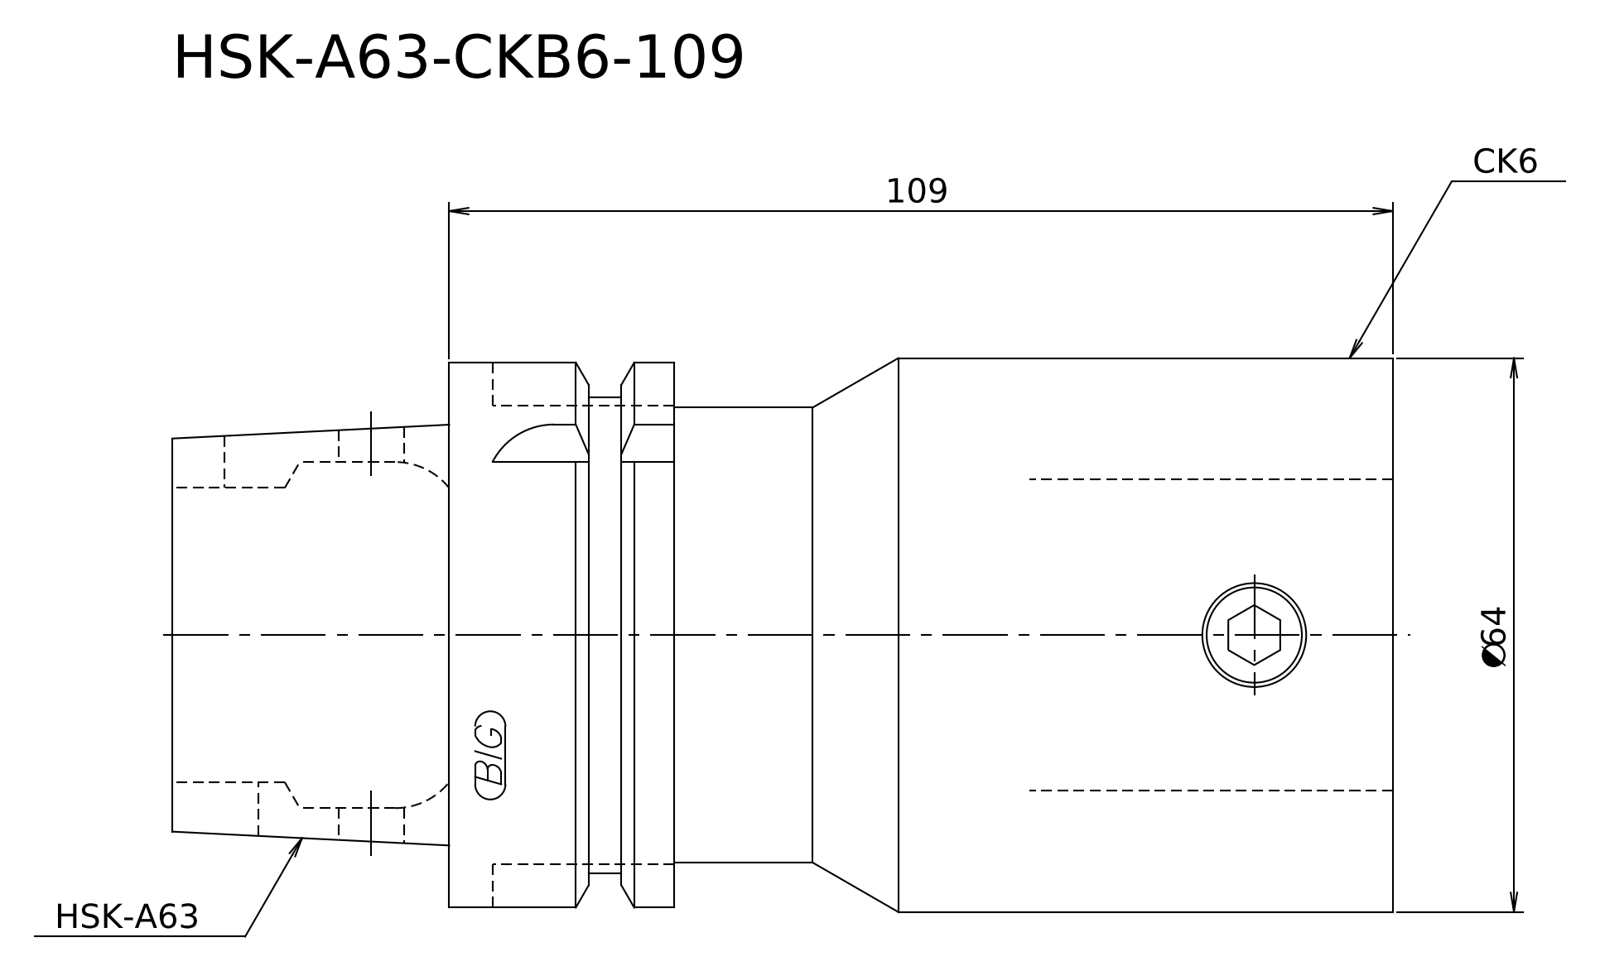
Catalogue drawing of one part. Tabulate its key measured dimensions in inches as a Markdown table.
| quantity | value |
| --- | --- |
| STEP written by | Kubotek KeyCreator V8.5.1 (14335) (CONFIG_CONTROL_DESIGN) |
| units | inches |
| bodies | 1 solid, 16 faces (6 planar, 6 cylindrical, 4 other) |
| overall size | 5.551 × 2.52 × 2.52 |
| volume | 23.07 in³ |
| surface area | 52.86 in² |
| round bosses / shafts (diameter × count) | 2.52 × 1, 2.48 × 1, 2.165 × 1, 2.071 × 1, 1.907 × 1 |
| main face-to-face distances | 5.551, 4.291, 1.26, 3.268, 1.024, 2.283, 3.509, 0.241, 0.783, 2.043 |
